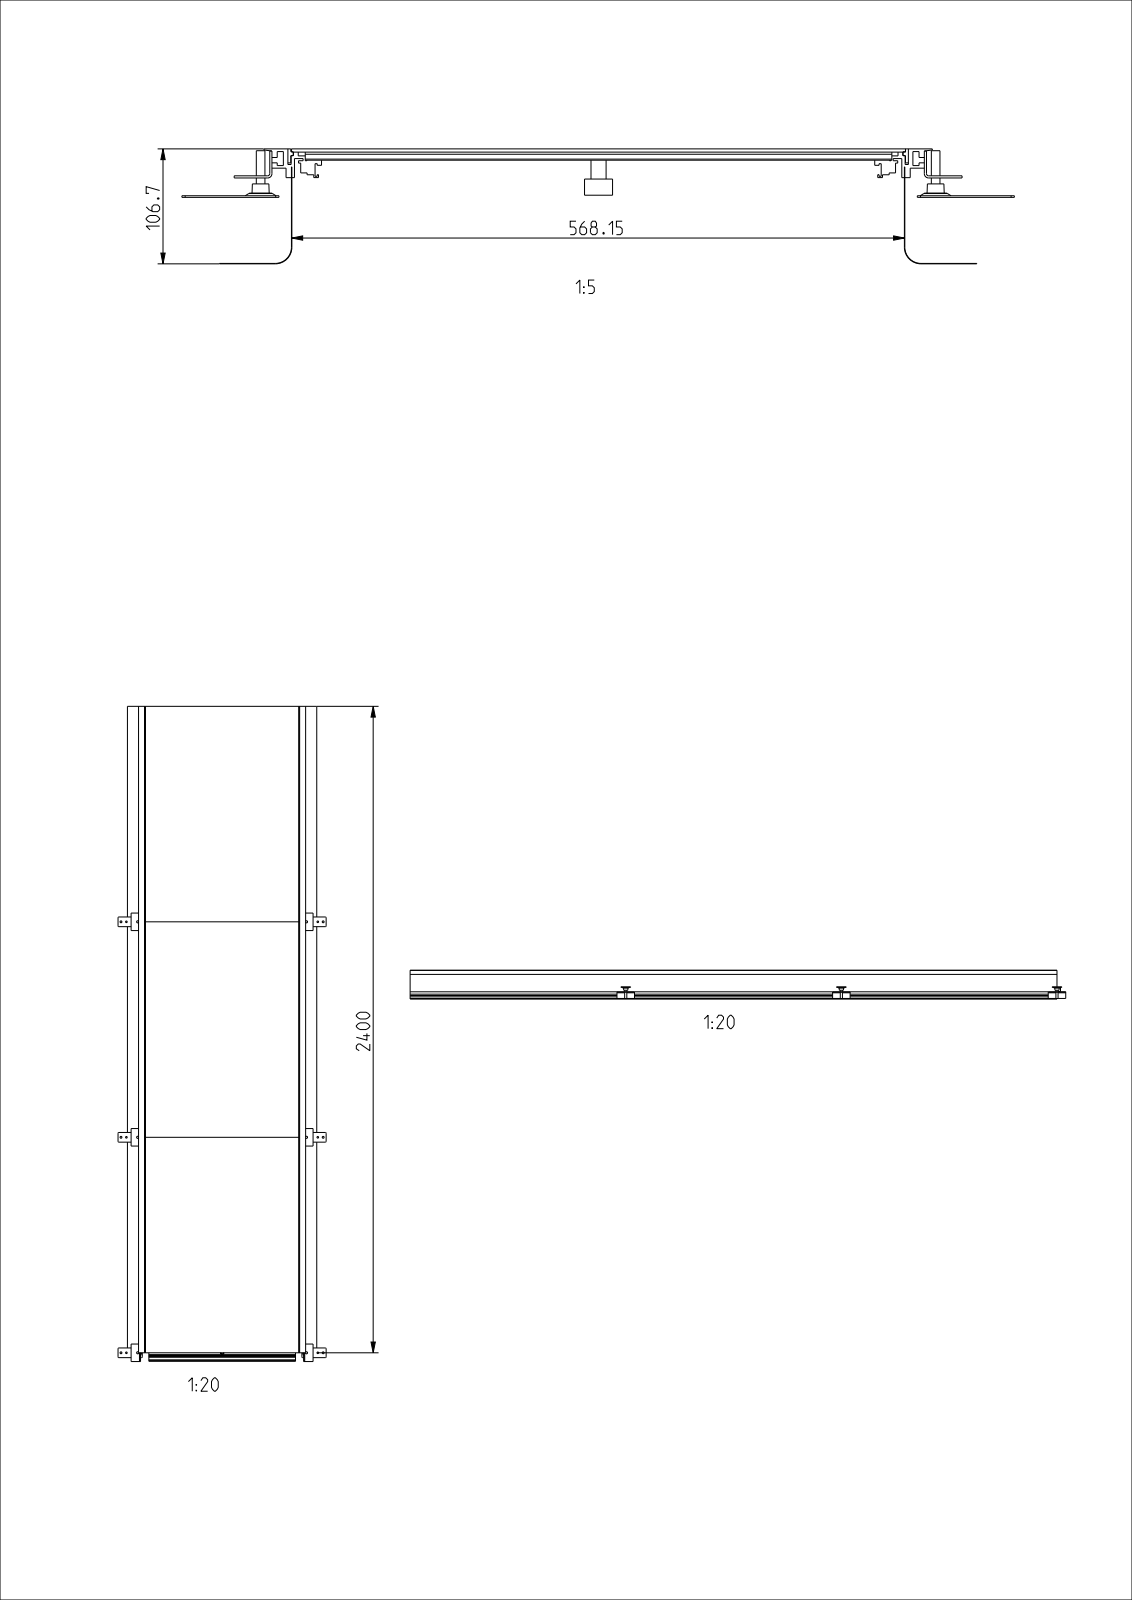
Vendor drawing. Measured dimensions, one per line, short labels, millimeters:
name: U05644KUN; U05650KUN; U05647KUN; U05826KUN (+8 more)
written by: CREO PARAMETRIC BY PTC INC, 2020281 (AUTOMOTIVE_DESIGN)
unit: mm
bodies: 62 solids, 1026 faces (600 planar, 354 cylindrical, 72 other)
size: 2432.5 × 772.13 × 106.7
volume: 8 915 000 mm³; area: 6 694 000 mm²
holes: 15× ⌀7, 9× ⌀8, 9× ⌀10, 6× ⌀6, 6× ⌀8.5, 6× ⌀11.5, 6× ⌀17.5, 6× ⌀23
bosses: 9× ⌀26, 9× ⌀14, 9× ⌀11.9, 6× ⌀20, 6× ⌀8
rounds: 92× R2, 24× R3, 20× R0.5, 2× R4, 2× R15, 2× R15.4
face distances: 3, 0.4, 568.55, 7.5, 6.5, 10.5, 4, 96.2, 103.7, 106.7
hole spacings: 800, 1600, 800.25, 801.1, 802.4, 1042.3, 1055.24, 1083.09
